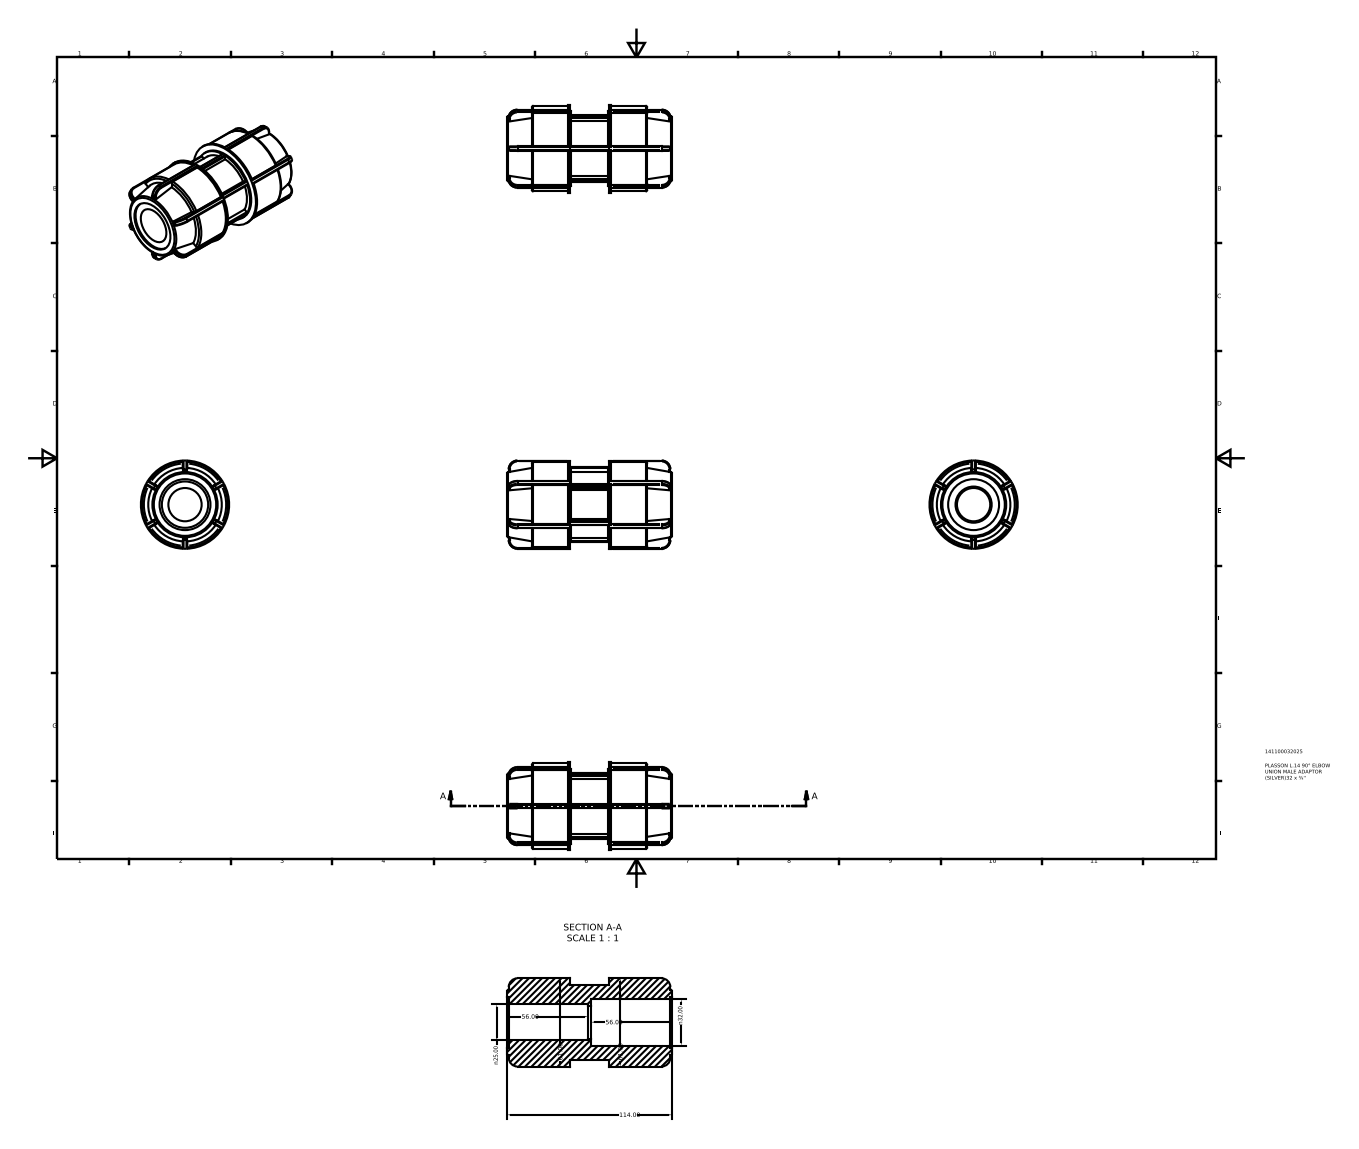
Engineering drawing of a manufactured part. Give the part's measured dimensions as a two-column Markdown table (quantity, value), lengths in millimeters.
| quantity | value |
| --- | --- |
| part name | 141100032025 |
| STEP written by | Autodesk Inventor 2015 (AUTOMOTIVE_DESIGN) |
| units | millimeters |
| bodies | 1 solid, 230 faces (92 planar, 86 cylindrical, 52 other) |
| overall size | 114 × 61 × 61 |
| volume | 183 748 mm³ |
| surface area | 38 926 mm² |
| round holes (diameter × count) | 23 × 1, 25 × 1, 32 × 1, 35.2 × 1 |
| round bosses / shafts (diameter × count) | 61 × 1, 59.17 × 1, 51.85 × 1, 45.75 × 1 |
| partial cylindrical surfaces (radius × count) | 0.61 × 44 |
| main face-to-face distances | 27.36, 1.14, 26.22, 43.32, 69.54, 70.68, 3.2, 42.18, 17.1, 96.9 |
